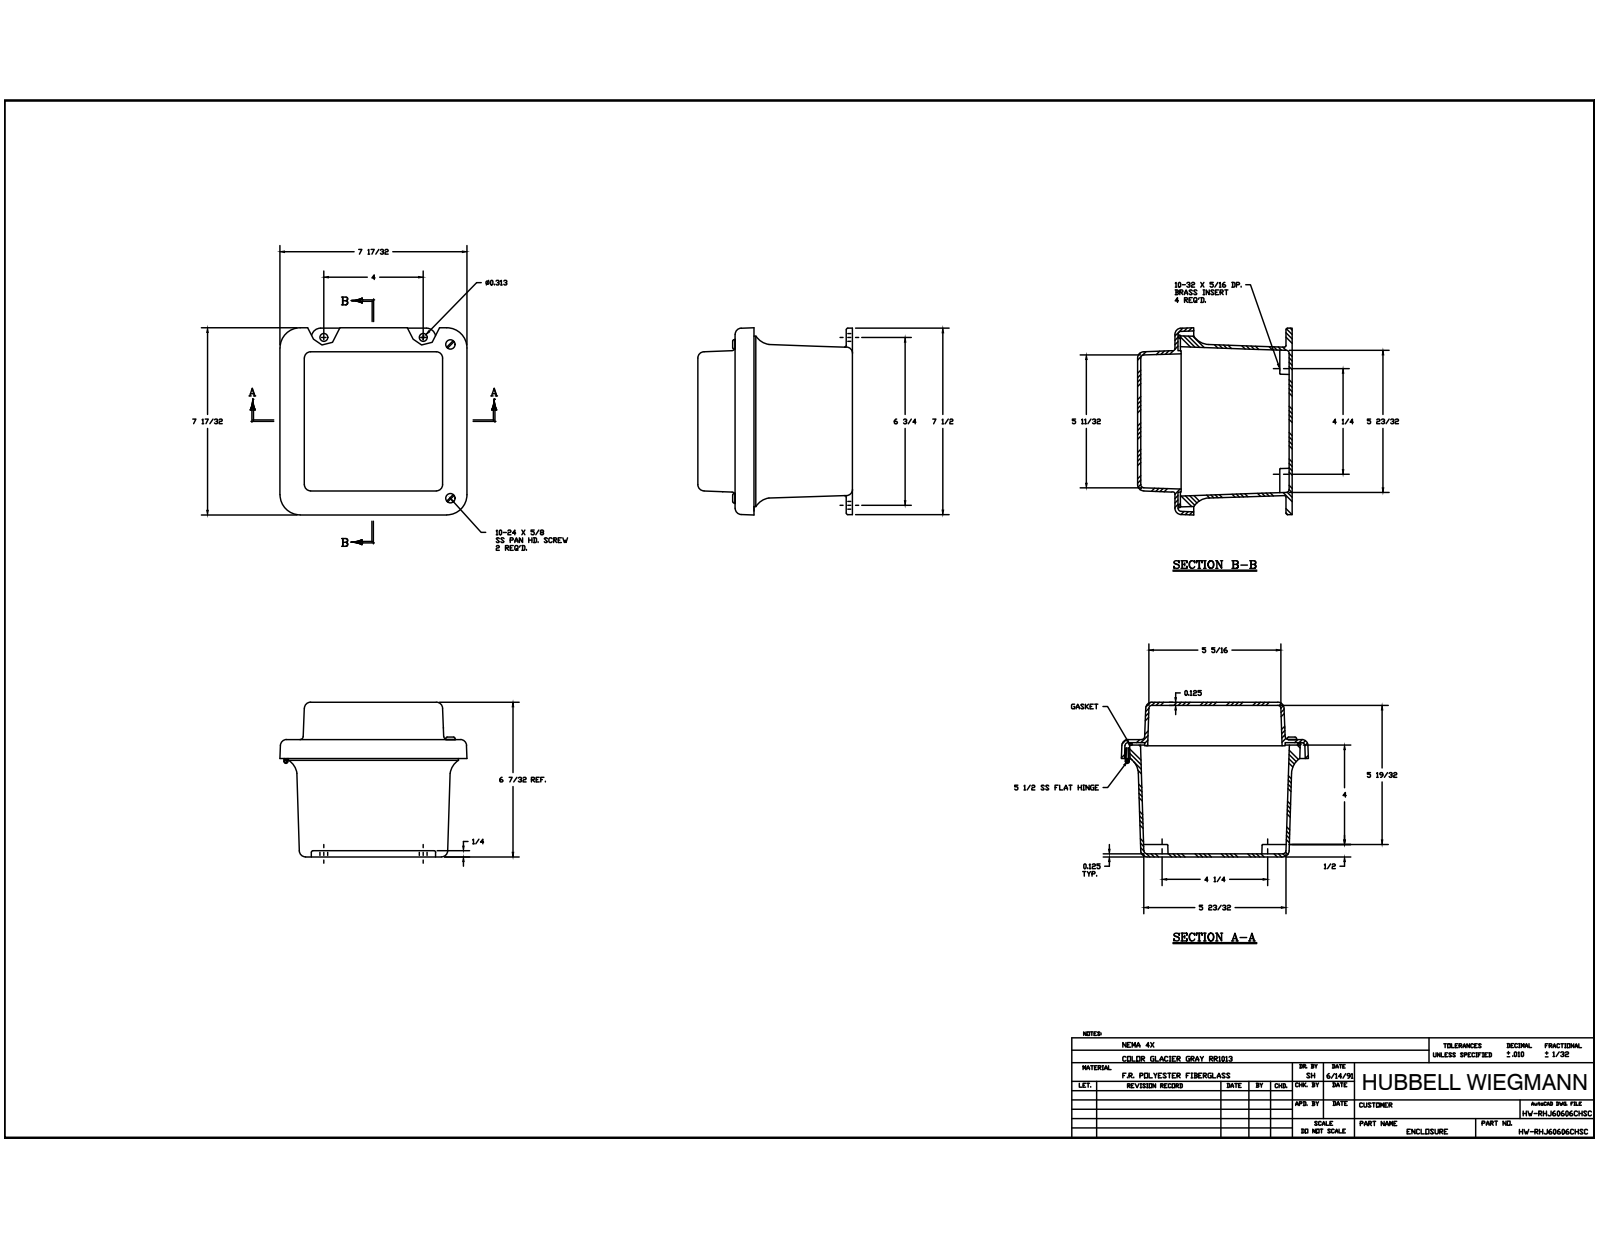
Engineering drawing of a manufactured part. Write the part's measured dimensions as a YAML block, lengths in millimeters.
part_name: "J606HW_2; RMINS45821P_119; RMINS45821P_120; RMINS45821P_121 (+8 more)"
step_written_by: "Autodesk Inventor 2014 (AUTOMOTIVE_DESIGN)"
units: millimeters
bodies: {solids: 19, faces: 716, planar: 223, cylindrical: 267, other: 226}
overall_size: [191.86, 191.13, 160.99]
volume: 660038
surface_area: 365179
round_holes:
  - {diameter: 3.33, count: 5}
  - {diameter: 3.56, count: 5}
  - {diameter: 3.86, count: 5}
  - {diameter: 3.96, count: 4}
  - {diameter: 5.54, count: 4}
  - {diameter: 3.68, count: 2}
  - {diameter: 2.16, count: 1}
round_bosses_or_shafts:
  - {diameter: 6.86, count: 6}
  - {diameter: 6.35, count: 5}
  - {diameter: 3.17, count: 5}
  - {diameter: 4.83, count: 2}
  - {diameter: 3.97, count: 2}
  - {diameter: 3.94, count: 1}
partial_cylinders:
  - {radius: 0.79, count: 20}
  - {radius: 3.17, count: 16}
  - {radius: 6.35, count: 16}
  - {radius: 1.59, count: 4}
  - {radius: 5.08, count: 4}
  - {radius: 7.91, count: 4}
  - {radius: 7.94, count: 4}
  - {radius: 9.53, count: 4}
face_to_face_distances: [3.18, 3.17, 38.1, 116.54, 154.64, 157.81, 160.99, 157.82, 119.71, 41.28]
hole_center_spacings: [134.82, 34.8, 63.5, 107.94, 157.16, 187.45, 12.7, 50.8]
